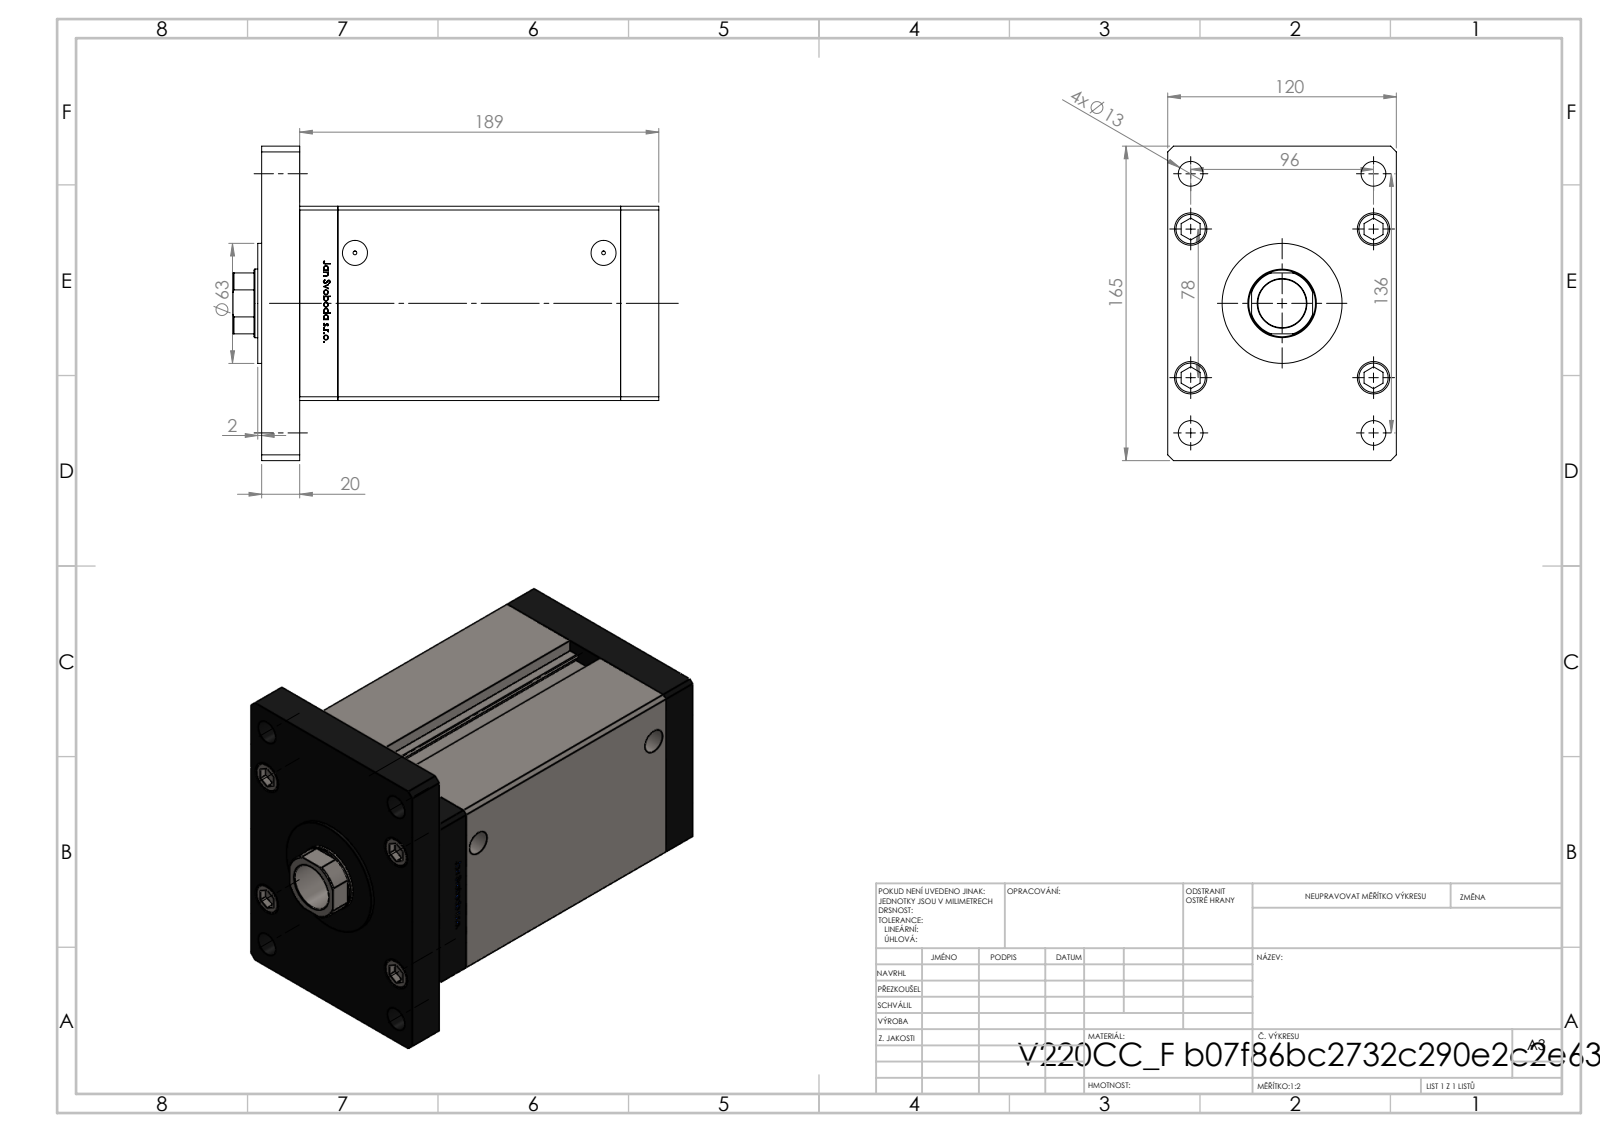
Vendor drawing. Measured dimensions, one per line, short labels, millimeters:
name: ALLEN BOLT; V220C_F; V220C_F_MIDDLE; V220C BACK_F (+2 more)
written by: SolidWorks 2019 (CONFIG_CONTROL_DESIGN)
unit: mm
bodies: 19 solids, 1311 faces (517 planar, 188 cylindrical, 606 other)
size: 223.5 × 165 × 120
volume: 2 417 000 mm³; area: 321 435 mm²
holes: 5× ⌀13.5, 5× ⌀18, 4× ⌀12, 4× ⌀13, 4× ⌀17, 2× ⌀2, 2× ⌀13.16, 1× ⌀25.5, 1× ⌀36, 1× ⌀37.5
bosses: 9× ⌀8, 5× ⌀17, 1× ⌀63
rounds: 2× R0.93, 1× R17.5
face distances: 20, 168.5, 188.5, 120, 102, 148.5, 40, 208.5, 34.25, 42
hole spacings: 41.5, 29, 61.85, 83.23, 96, 100.28, 107, 143.75
